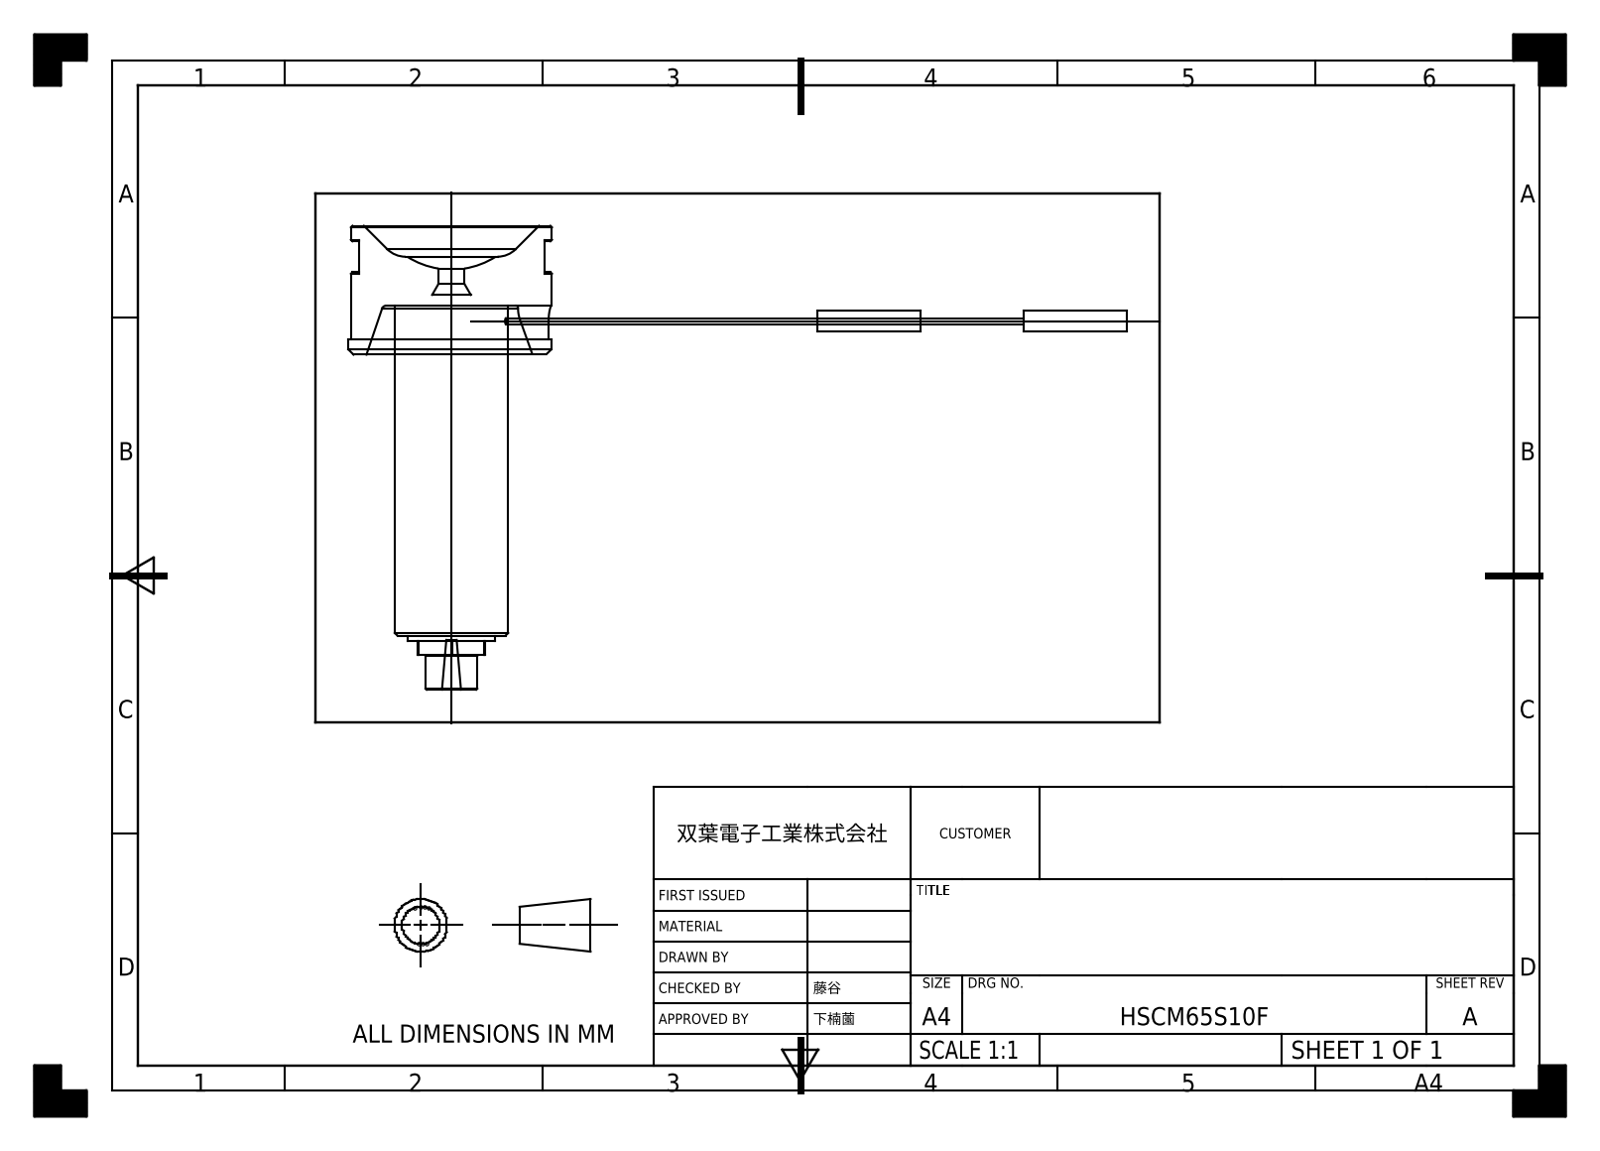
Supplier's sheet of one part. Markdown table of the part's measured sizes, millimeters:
| quantity | value |
| --- | --- |
| part name | HSCM65S10F |
| STEP written by | SIEMENS PLM Software NX 2023 (AUTOMOTIVE_DESIGN) |
| units | millimeters |
| bodies | 1 solid, 63 faces (29 planar, 18 cylindrical, 16 other) |
| overall size | 151 × 90 × 40 |
| volume | 44 700 mm³ |
| surface area | 12 435 mm² |
| round holes (diameter × count) | 5 × 1 |
| round bosses / shafts (diameter × count) | 4 × 2, 1.2 × 2, 40 × 1, 39 × 1, 22 × 1, 16.9 × 1, 10 × 1 |
| partial cylindrical surfaces (radius × count) | 3 × 2, 7.45 × 1 |
| main face-to-face distances | 25, 9.5, 15.5, 65, 79.5, 64, 54.5, 3, 36, 13 |
